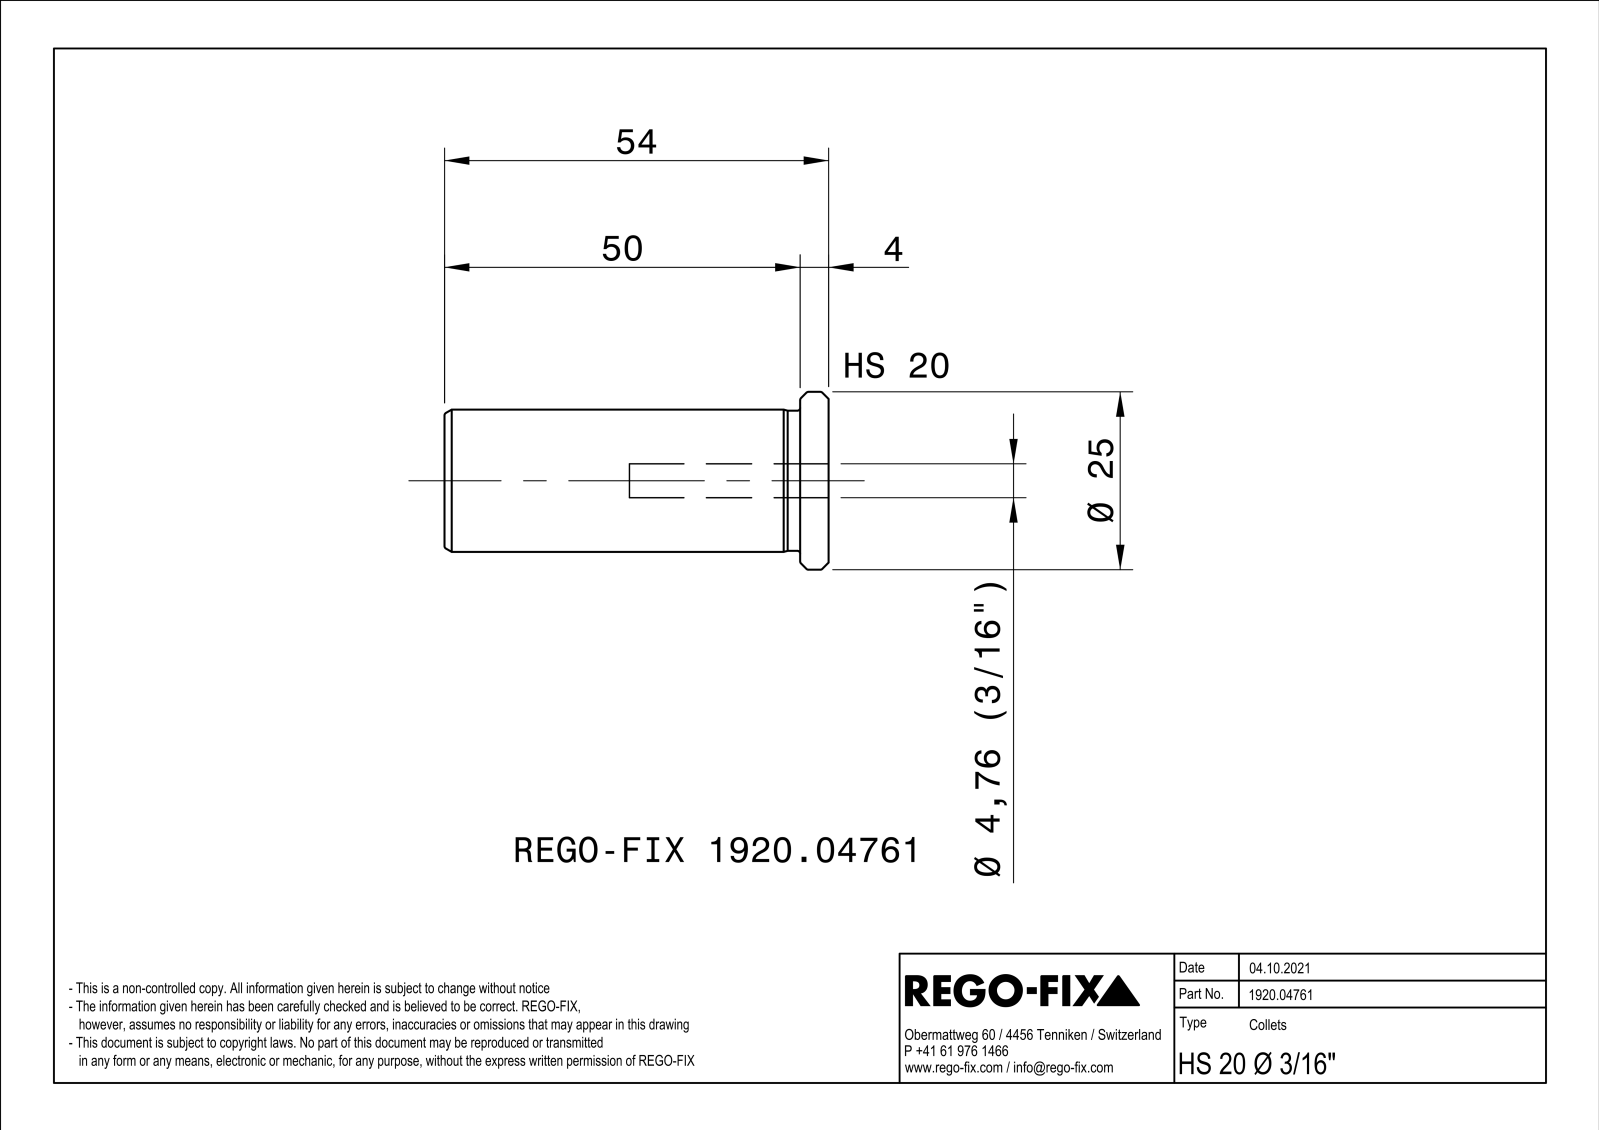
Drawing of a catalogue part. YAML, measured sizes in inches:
part_name: "NOCUT"
step_written_by: "SIEMENS PLM Software Solid Edge ST10 (AUTOMOTIVE_DESIGN)"
units: inches
bodies: {solids: 1, faces: 72, planar: 22, cylindrical: 12, other: 38}
overall_size: [2.126, 0.984, 0.984]
volume: 0.791
surface_area: 11.07
round_holes:
  - {diameter: 0.187, count: 1}
  - {diameter: 0.394, count: 1}
  - {diameter: 0.65, count: 1}
round_bosses_or_shafts:
  - {diameter: 0.984, count: 1}
  - {diameter: 0.787, count: 1}
  - {diameter: 0.776, count: 1}
face_to_face_distances: [0.031, 0.157, 2.126, 1.969]
